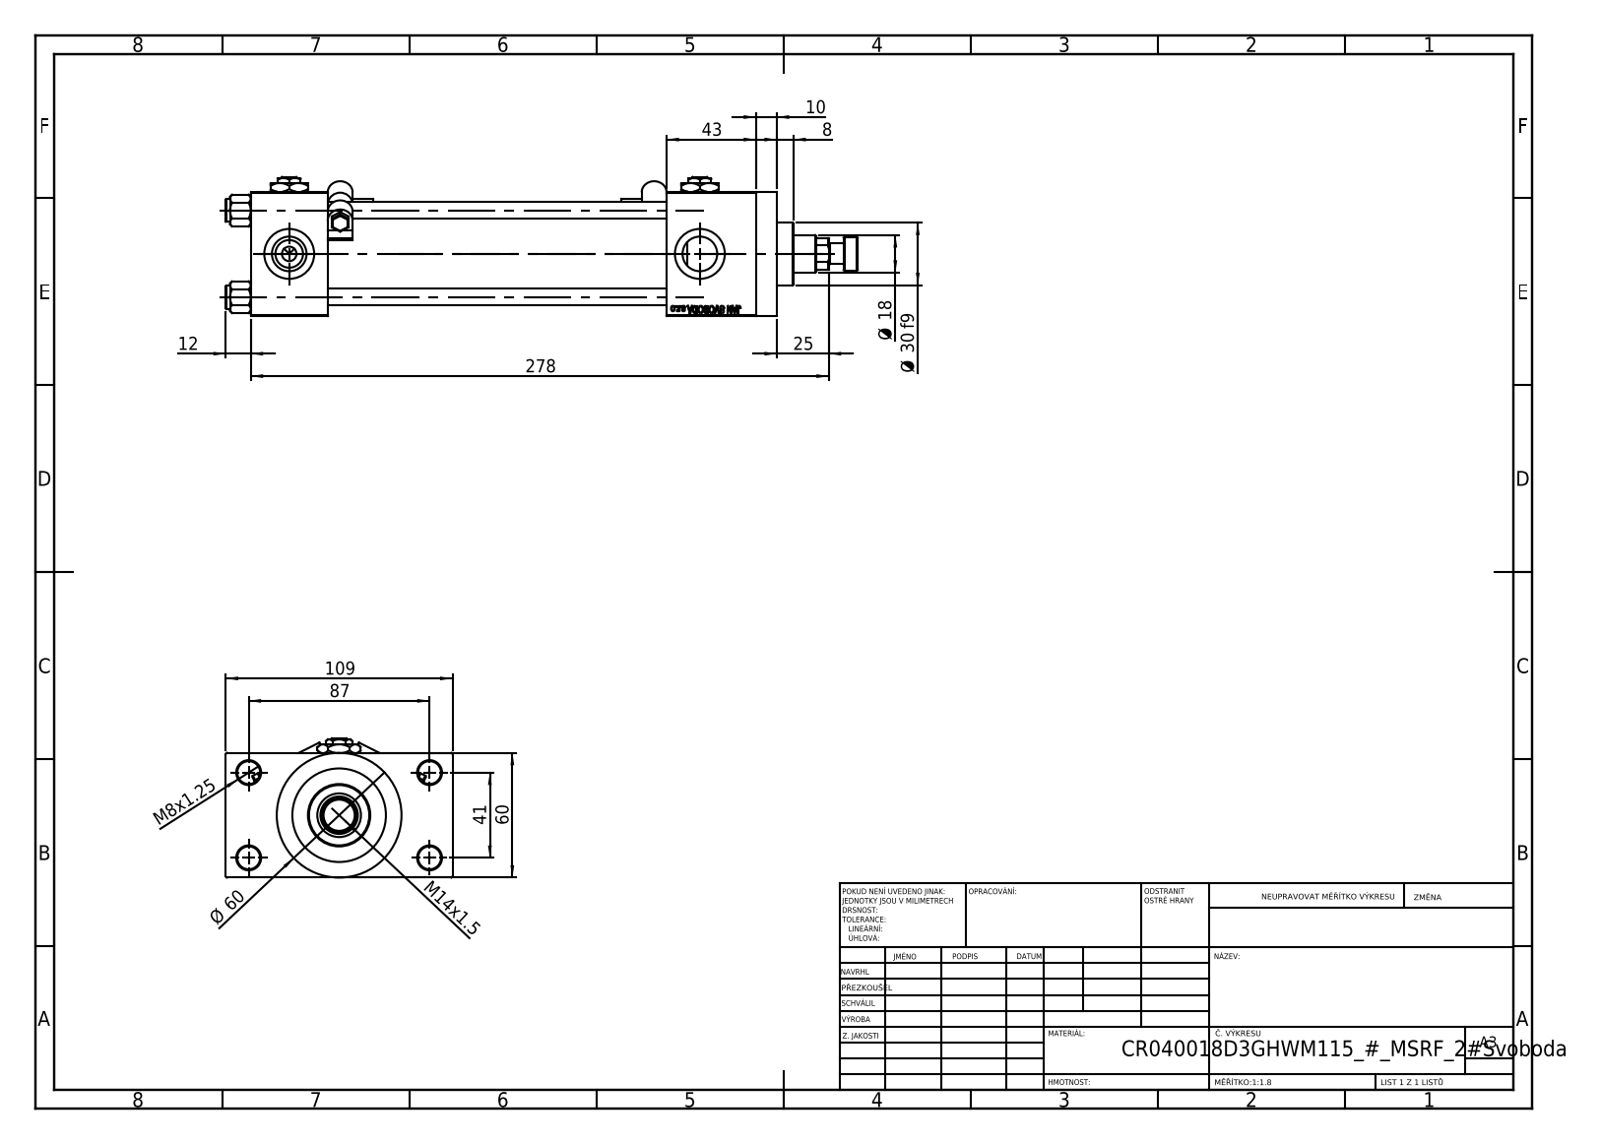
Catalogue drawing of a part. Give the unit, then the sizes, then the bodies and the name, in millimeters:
Units: millimetres
Overall size (bounding box): 304 × 109 × 67
Round holes (diameter × count): ⌀8 ×4, ⌀11 ×4, ⌀16.66 ×4, ⌀24 ×4, ⌀7 ×3, ⌀8.5 ×1, ⌀18 ×1, ⌀21 ×1, ⌀31 ×1, ⌀40 ×1, ⌀45 ×1
Round bosses / shafts (diameter × count): ⌀11 ×4, ⌀5 ×2, ⌀2.5 ×2, ⌀60 ×1, ⌀46 ×1, ⌀30 ×1, ⌀16 ×1, ⌀10 ×1
Partial cylindrical surfaces — rounded edges, fillets, slot ends (radius × count): R0.5 ×12, R6 ×4, R8.5 ×1
Main face-to-face distances: 60, 163, 24.5, 200, 84.5, 37, 243, 43, 206, 10
Hole centre spacings: 22.65, 29.49, 41.7, 47.15, 48.09, 64.35, 76.49, 41
Volume: 609 750 mm³ · Surface area: 175 323 mm²
Bodies: 16 solids, 1282 faces (585 planar, 131 cylindrical, 566 other)
Part name (STEP PRODUCT): V215CR_D_Body; V215CR_VCP_D; MSRF_MSRG1; NUT_M5_D (+4 more)
STEP written by: SolidWorks 2019 (CONFIG_CONTROL_DESIGN)
